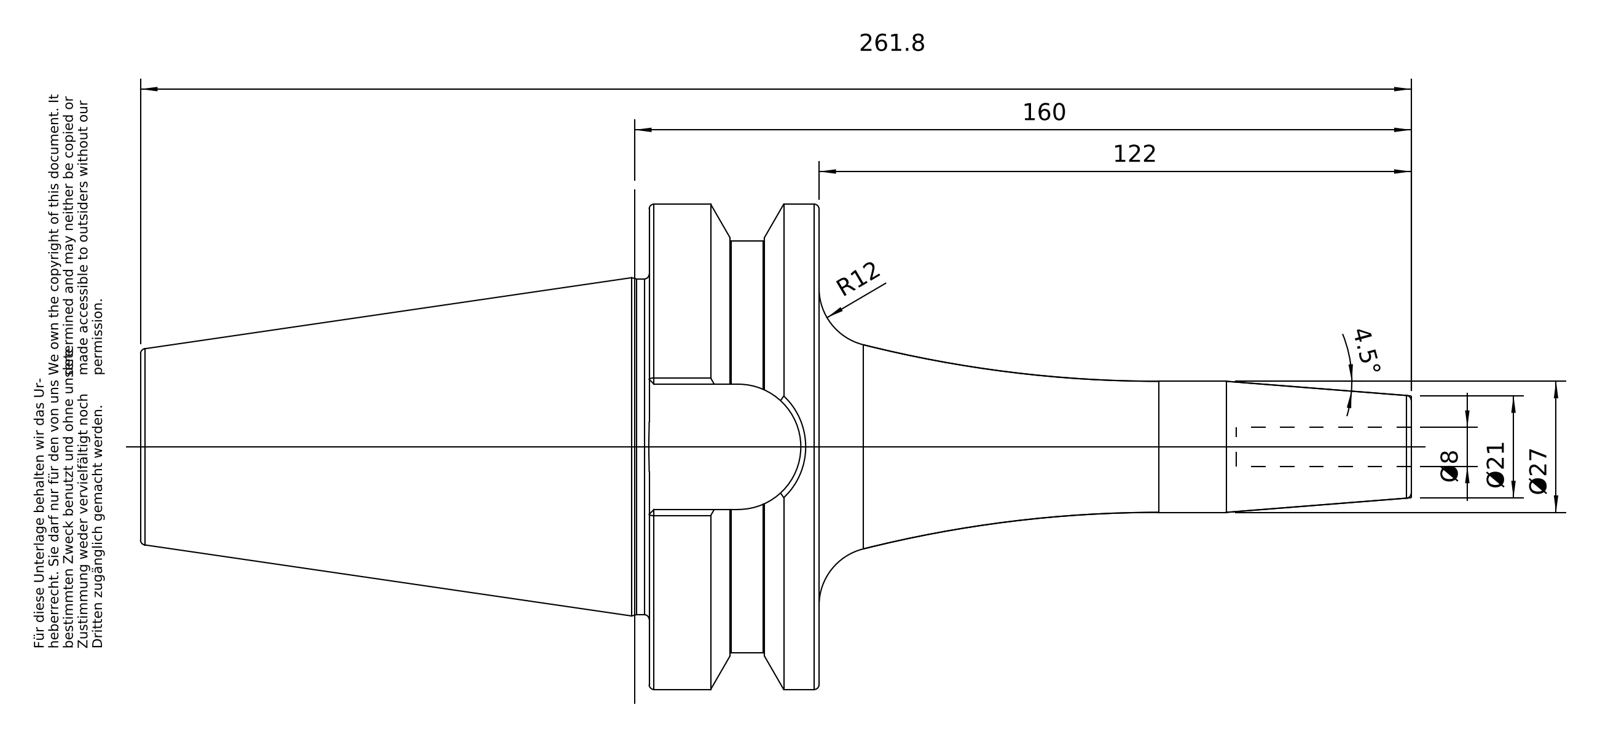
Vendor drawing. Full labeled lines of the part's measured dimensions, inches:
Part name (STEP PRODUCT): 50-642-08
STEP written by: PRO/ENGINEER BY PARAMETRIC TECHNOLOGY CORPORATION, 2010430 (CONFIG_CONTROL_DESIGN)
Units: inches
Bodies: 1 solid, 98 faces (26 planar, 22 cylindrical, 50 other)
Overall size (bounding box): 10.307 × 3.936 × 3.936
Volume: 34.06 in³ · Surface area: 96.96 in²
Round holes (diameter × count): ⌀0.315 ×1, ⌀0.817 ×1, ⌀0.985 ×1, ⌀1.012 ×1
Round bosses / shafts (diameter × count): ⌀3.936 ×1, ⌀3.337 ×1, ⌀2.722 ×1, ⌀1.063 ×1, ⌀0.945 ×1
Partial cylindrical surfaces — rounded edges, fillets, slot ends (radius × count): R0.508 ×1
Main face-to-face distances: 1.378, 2.772, 4.126, 5.504, 1.016, 10.307, 6.181, 4.803, 1.89, 2.236
